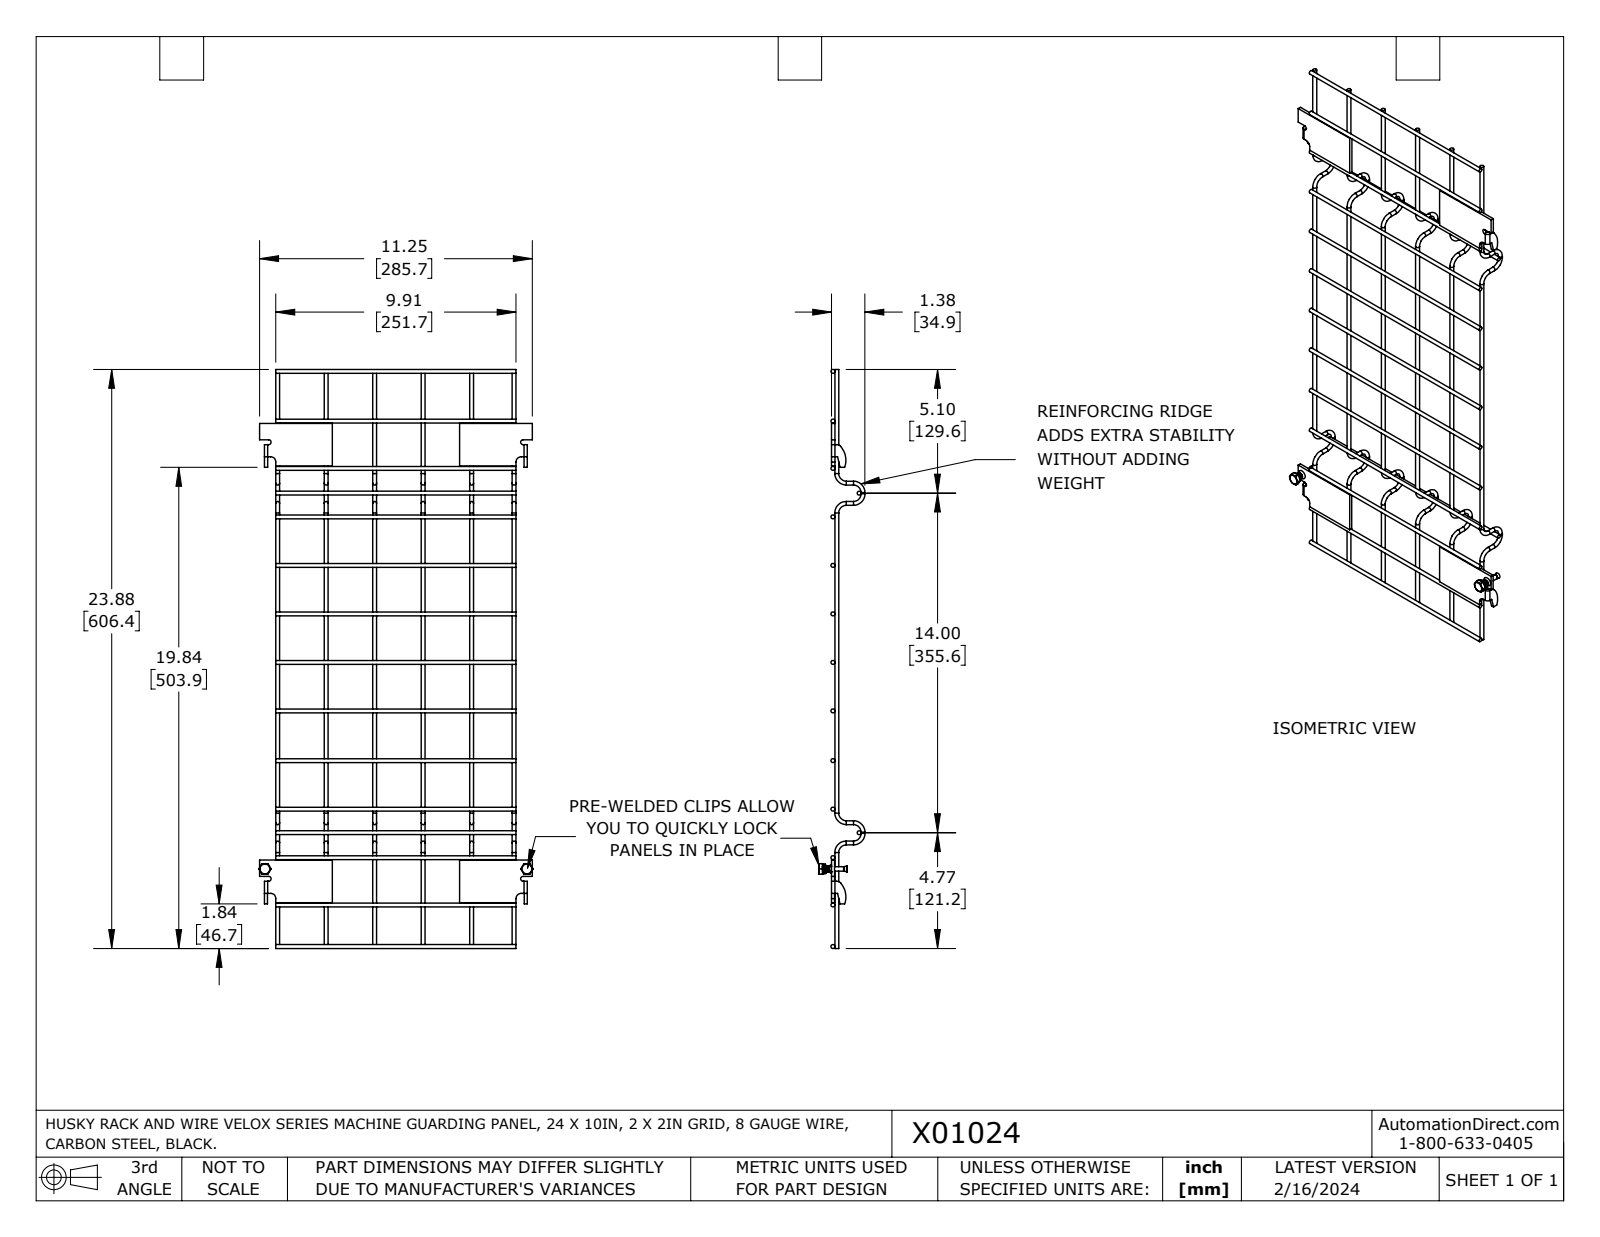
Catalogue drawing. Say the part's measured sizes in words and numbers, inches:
The part is named "X01024". Its 3-D file was written by "SolidWorks 2023 (AUTOMOTIVE_DESIGN)". It is 29 solids with 299 faces: 122 planar, 105 cylindrical and 72 other. Overall it measures 23.875 by 11.313 by 1.853 inches. Its volume is 9.006 cubic inches and its surface area 206.7 square inches. Round holes: 2 of diameter 0.201, 2 of diameter 0.25. Round bosses or shafts: 51 of diameter 0.16, 2 of diameter 0.39, 2 of diameter 0.245, 2 of diameter 0.187. Partial cylindrical surfaces (rounded edges, fillets, slot ends): 4 of radius 0.1, 4 of radius 0.218, 2 of radius 0.009, 2 of radius 0.067, 2 of radius 0.134, 2 of radius 0.25, 2 of radius 0.865. The main face-to-face distances are 0.134, 0.125, 2.798, 8.046, 18, 18, 0.467, 10.377, 2.331, 7.579. The hole center spacings are 10.808.
